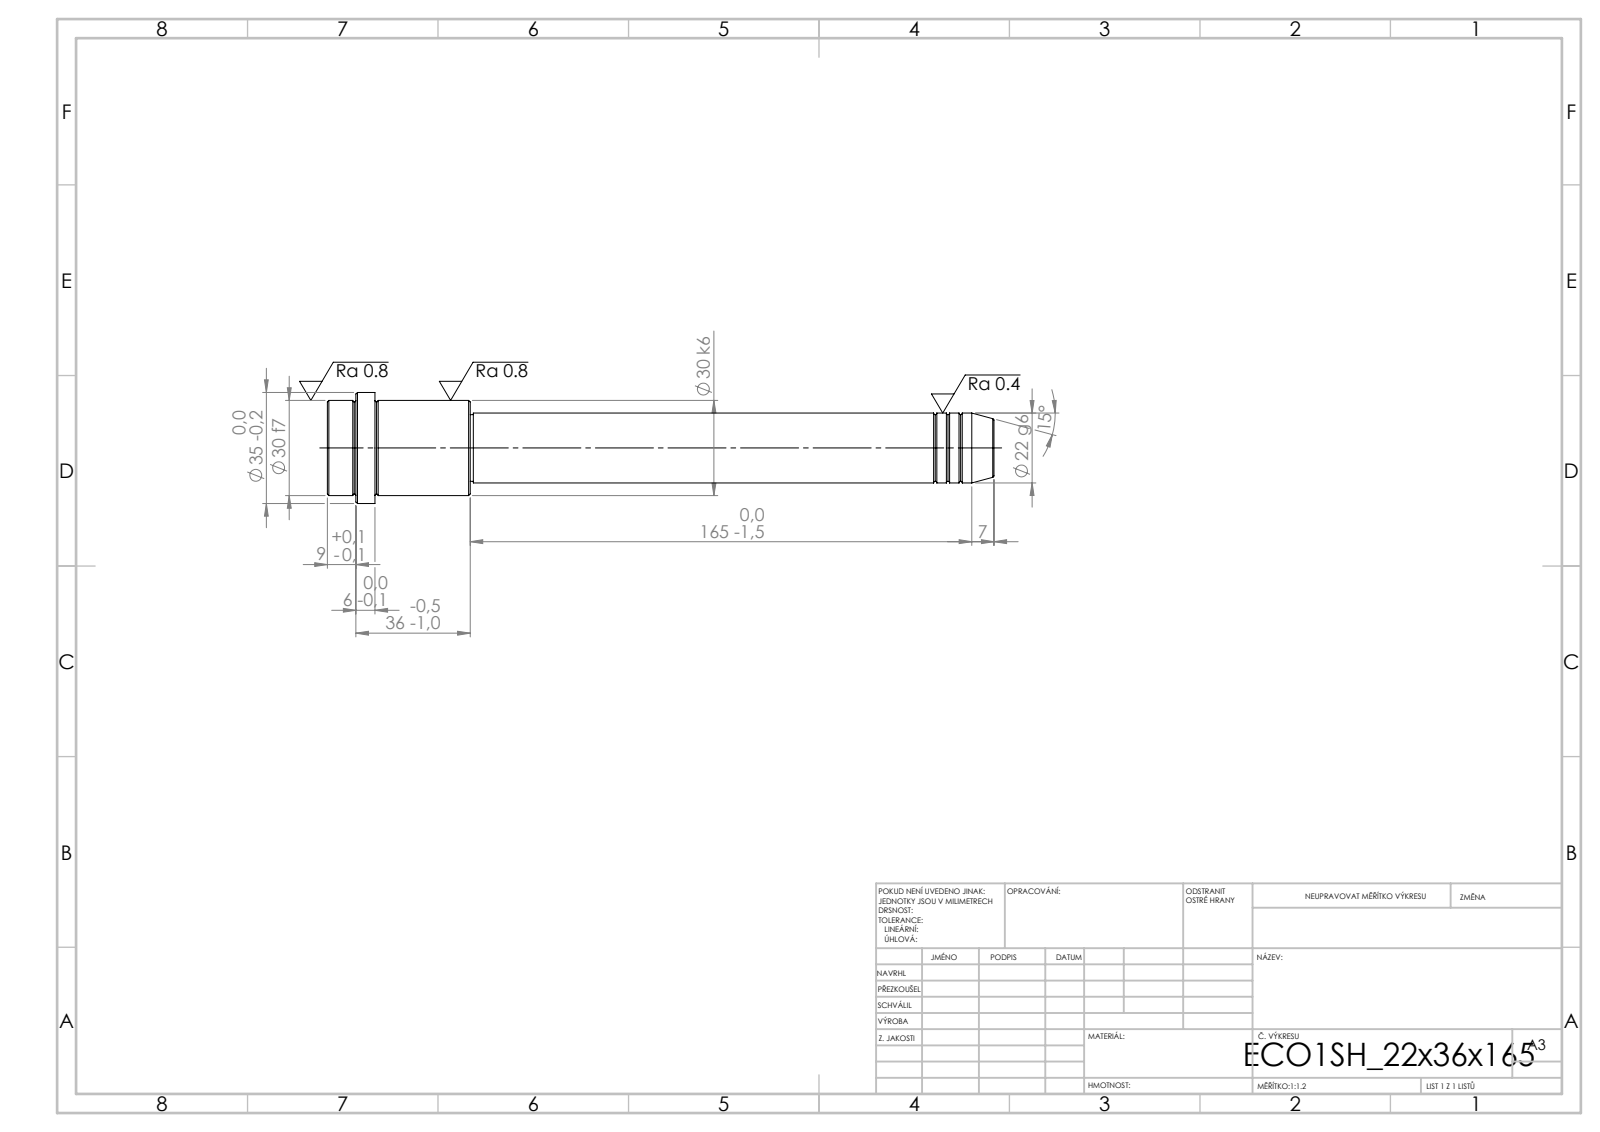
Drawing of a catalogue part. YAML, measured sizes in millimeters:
step_written_by: "SolidWorks 2019 (CONFIG_CONTROL_DESIGN)"
units: millimeters
bodies: {solids: 1, faces: 52, planar: 6, cylindrical: 16, other: 30}
overall_size: [210, 35, 35]
volume: 95409
surface_area: 17699
round_bosses_or_shafts:
  - {diameter: 35, count: 1}
  - {diameter: 30, count: 1}
  - {diameter: 22, count: 1}
  - {diameter: 21, count: 1}
face_to_face_distances: [45, 30, 15, 165, 195, 210, 201, 36, 6, 9]
